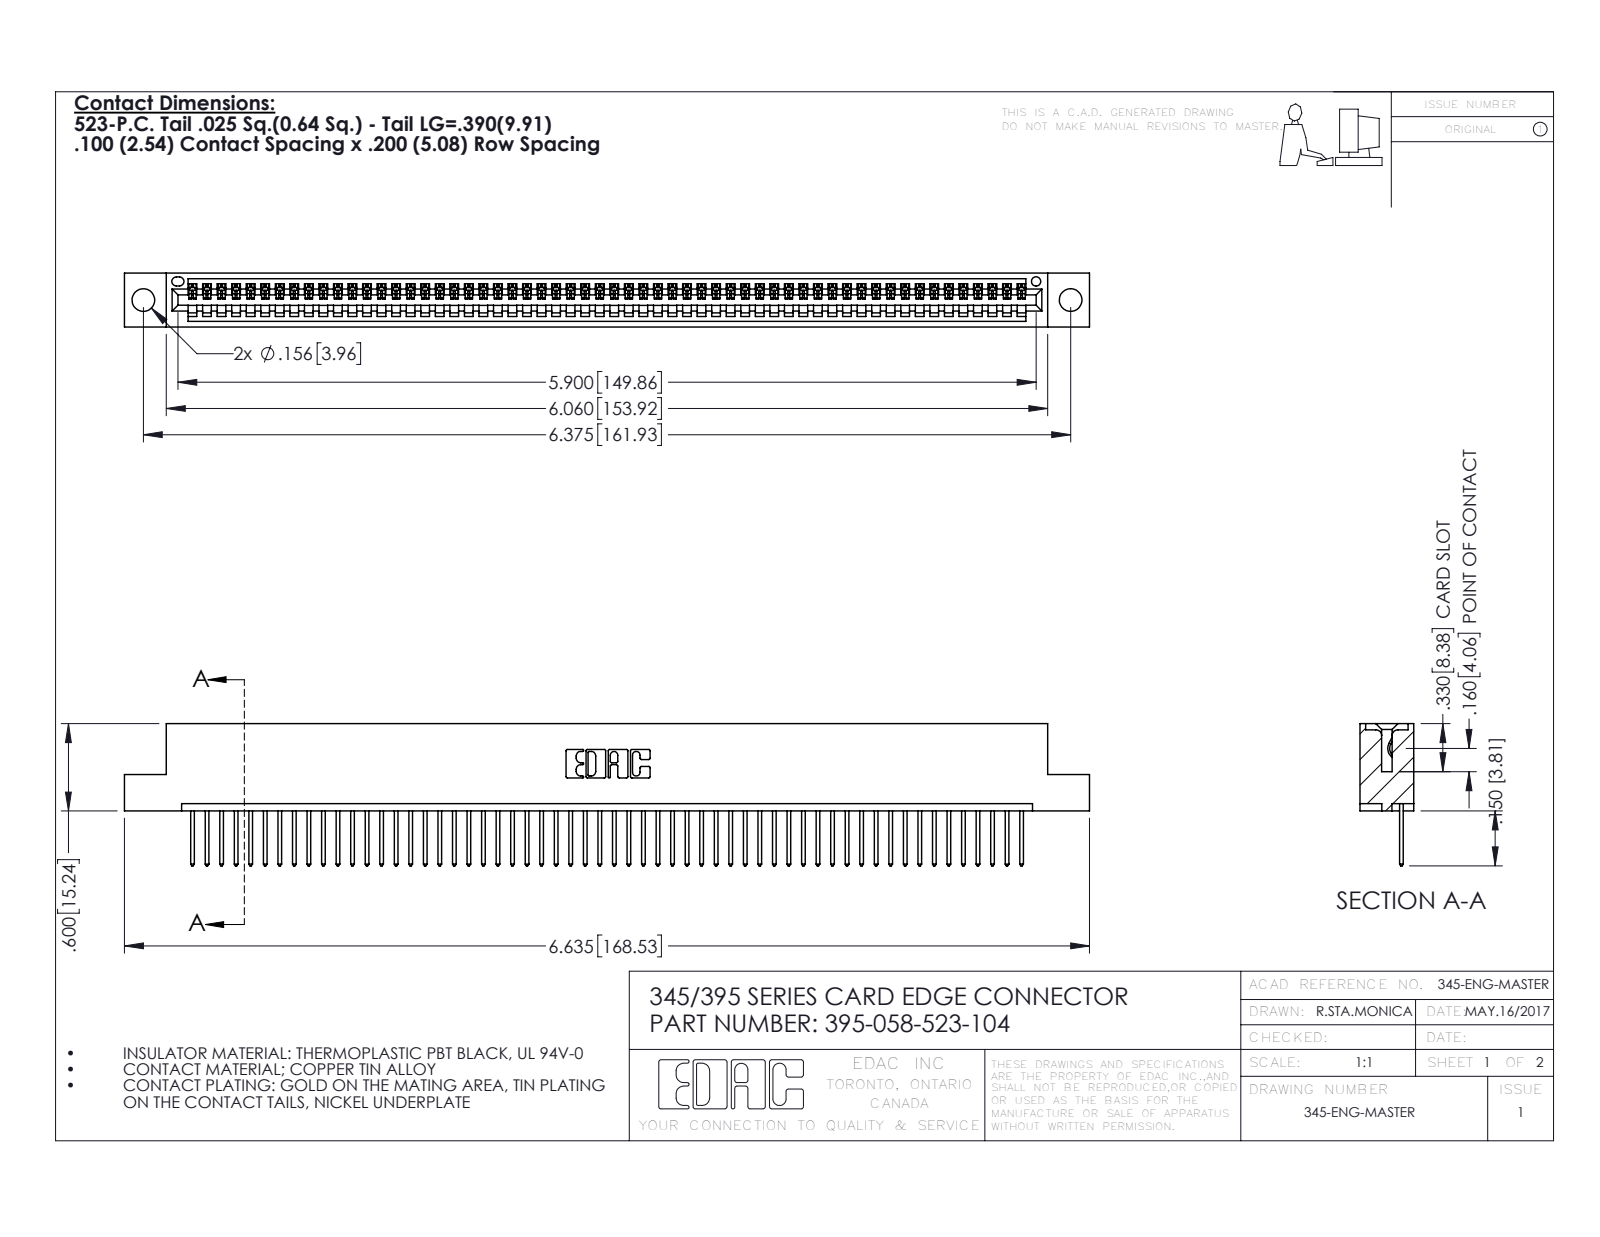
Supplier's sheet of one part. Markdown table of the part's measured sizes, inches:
| quantity | value |
| --- | --- |
| part name | 345-292-001_345-293-123; 345 Part_Flush Mounting Lugs - 0.156 Dia-TH; 395-058-523-104 |
| STEP written by | SolidWorks 2016 (CONFIG_CONTROL_DESIGN) |
| units | inches |
| bodies | 59 solids, 3490 faces (2400 planar, 1090 cylindrical, 0 other) |
| overall size | 6.635 × 0.977 × 0.37 |
| volume | 0.978 in³ |
| surface area | 33.15 in² |
| round holes (diameter × count) | 0.156 × 2, 0.064 × 1 |
| partial cylindrical surfaces (radius × count) | 0.006 × 116, 0.01 × 116, 0.01 × 22, 0.007 × 6, 0.031 × 6, 0.026 × 3, 0.031 × 2, 0.04 × 2 |
| main face-to-face distances | 0.298, 0.072, 0.37, 0.2, 0.098, 0.272, 0.025, 0.225, 0.149, 0.072 |
| hole center spacings | 0.27, 6.139, 6.375 |
